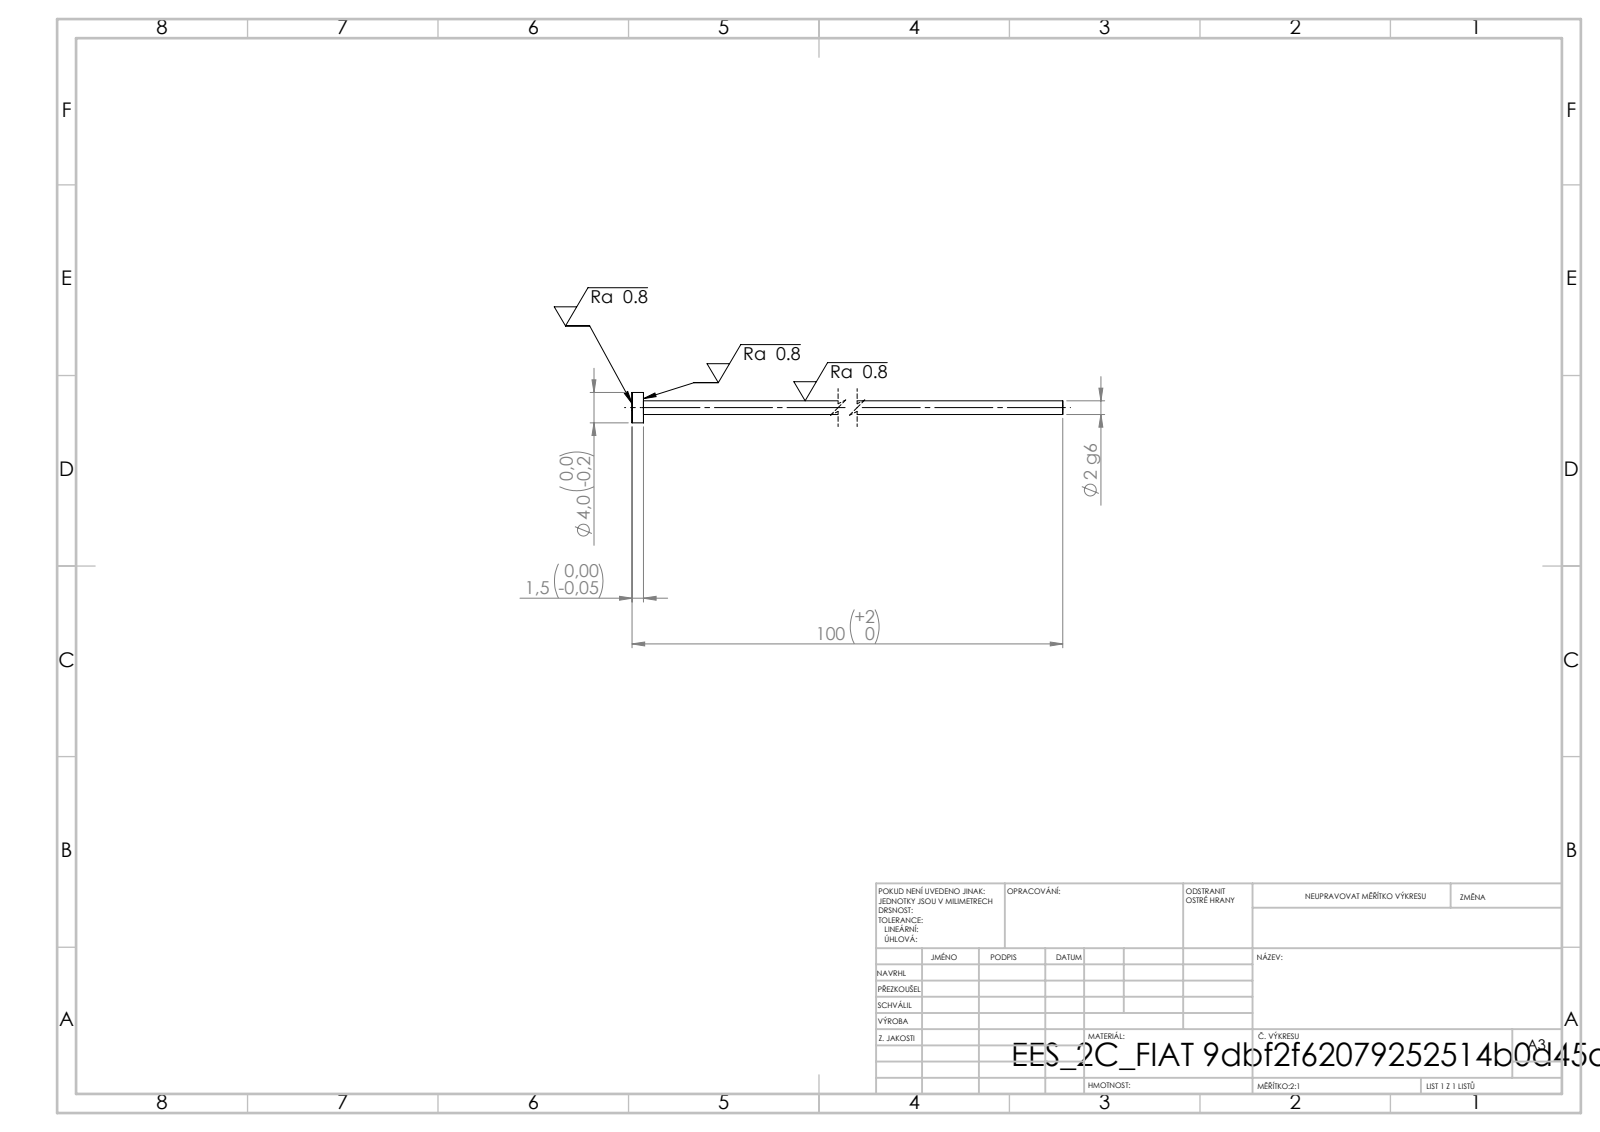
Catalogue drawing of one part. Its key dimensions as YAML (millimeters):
step_written_by: "SolidWorks 2019 (CONFIG_CONTROL_DESIGN)"
units: millimeters
bodies: {solids: 1, faces: 7, planar: 3, cylindrical: 4, other: 0}
overall_size: [100, 4, 4]
volume: 270
surface_area: 601
round_bosses_or_shafts:
  - {diameter: 4, count: 1}
  - {diameter: 1.8, count: 1}
face_to_face_distances: [1.5, 100, 98.5]
